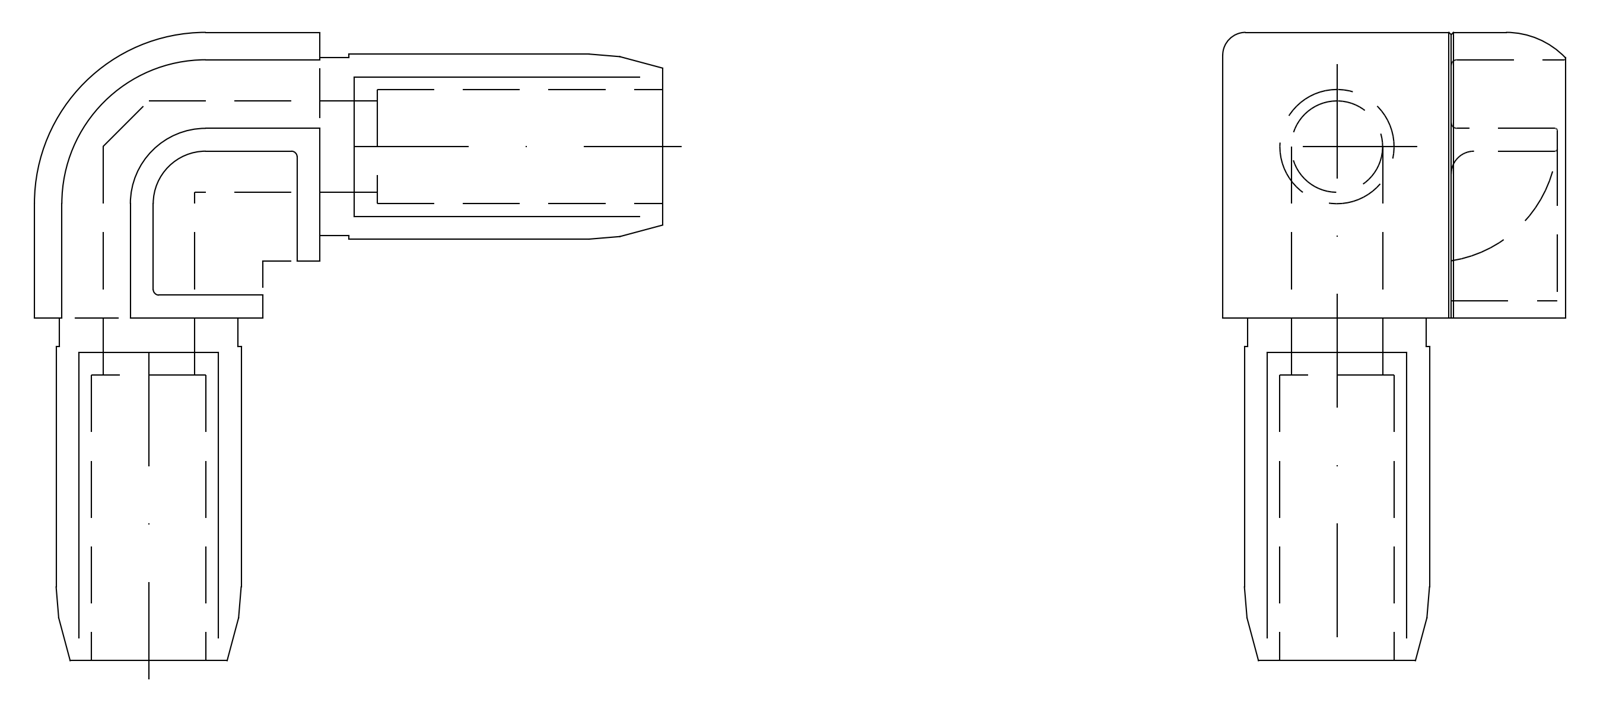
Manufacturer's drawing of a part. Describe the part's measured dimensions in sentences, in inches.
Its 3-D file was written by "THINKDESIGN (CONFIG_CONTROL_DESIGN)". It is 1 solid with 112 faces: 70 planar, 23 cylindrical and 19 other. Overall it measures 2.165 by 2.165 by 1.178 inches. Its volume is 1.415 cubic inches and its surface area 15.79 square inches. Round holes: 2 of diameter 0.315. Partial cylindrical surfaces (rounded edges, fillets, slot ends): 5 of radius 0.118, 3 of radius 0.052, 3 of radius 0.052, 2 of radius 0.02, 2 of radius 0.052, 2 of radius 0.197, 1 of radius 0.181, 1 of radius 0.26. The main face-to-face distances are 0.075, 0.713, 0.638, 0.079, 0.272, 0.909, 0.575, 0.984, 0.087, 0.701.
